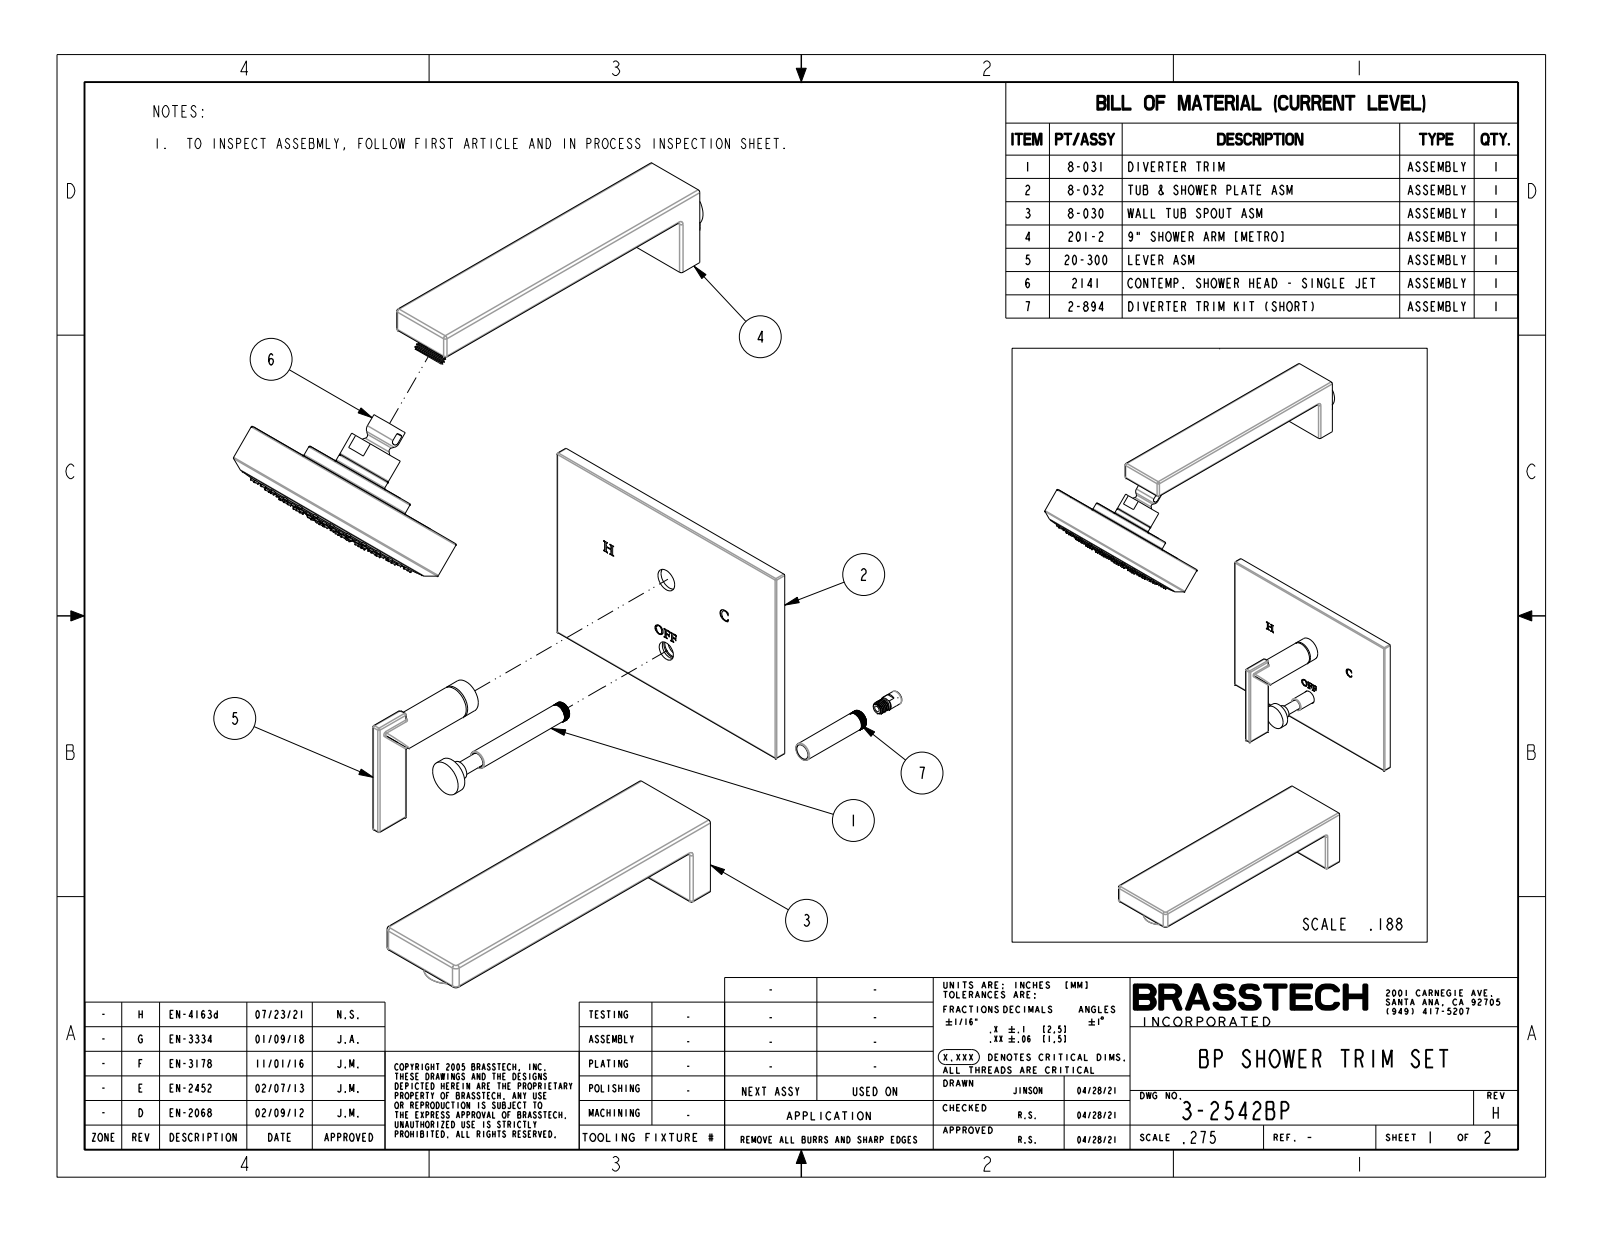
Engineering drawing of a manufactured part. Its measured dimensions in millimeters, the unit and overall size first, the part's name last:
Units: millimetres
Overall size (bounding box): 541 × 317.3 × 196.9
Round holes (diameter × count): ⌀1.3 ×90, ⌀5.6 ×1, ⌀8.8 ×1, ⌀133.5 ×1
Round bosses / shafts (diameter × count): ⌀35.6 ×2, ⌀150.1 ×1, ⌀132.6 ×1, ⌀74.2 ×1, ⌀31.8 ×1, ⌀23 ×1, ⌀22.9 ×1, ⌀21.8 ×1
Partial cylindrical surfaces — rounded edges, fillets, slot ends (radius × count): R1.5 ×21, R1 ×16, R0.8 ×8, R2 ×2, R3 ×2, R12.1 ×1
Main face-to-face distances: 7.9, 17, 485.1, 502.2, 485.5, 468.5, 16.6, 9.5, 54, 63.5
Hole centre spacings: 57.7, 46.7, 12.2, 24.2, 46.7, 12, 56.9, 35.6
Volume: 1 321 000 mm³ · Surface area: 207 700 mm²
Bodies: 3 solids, 1223 faces (185 planar, 268 cylindrical, 770 other)
Part name (STEP PRODUCT): 3-2542BP
STEP written by: CREO PARAMETRIC BY PTC INC, 2018400 (CONFIG_CONTROL_DESIGN)
